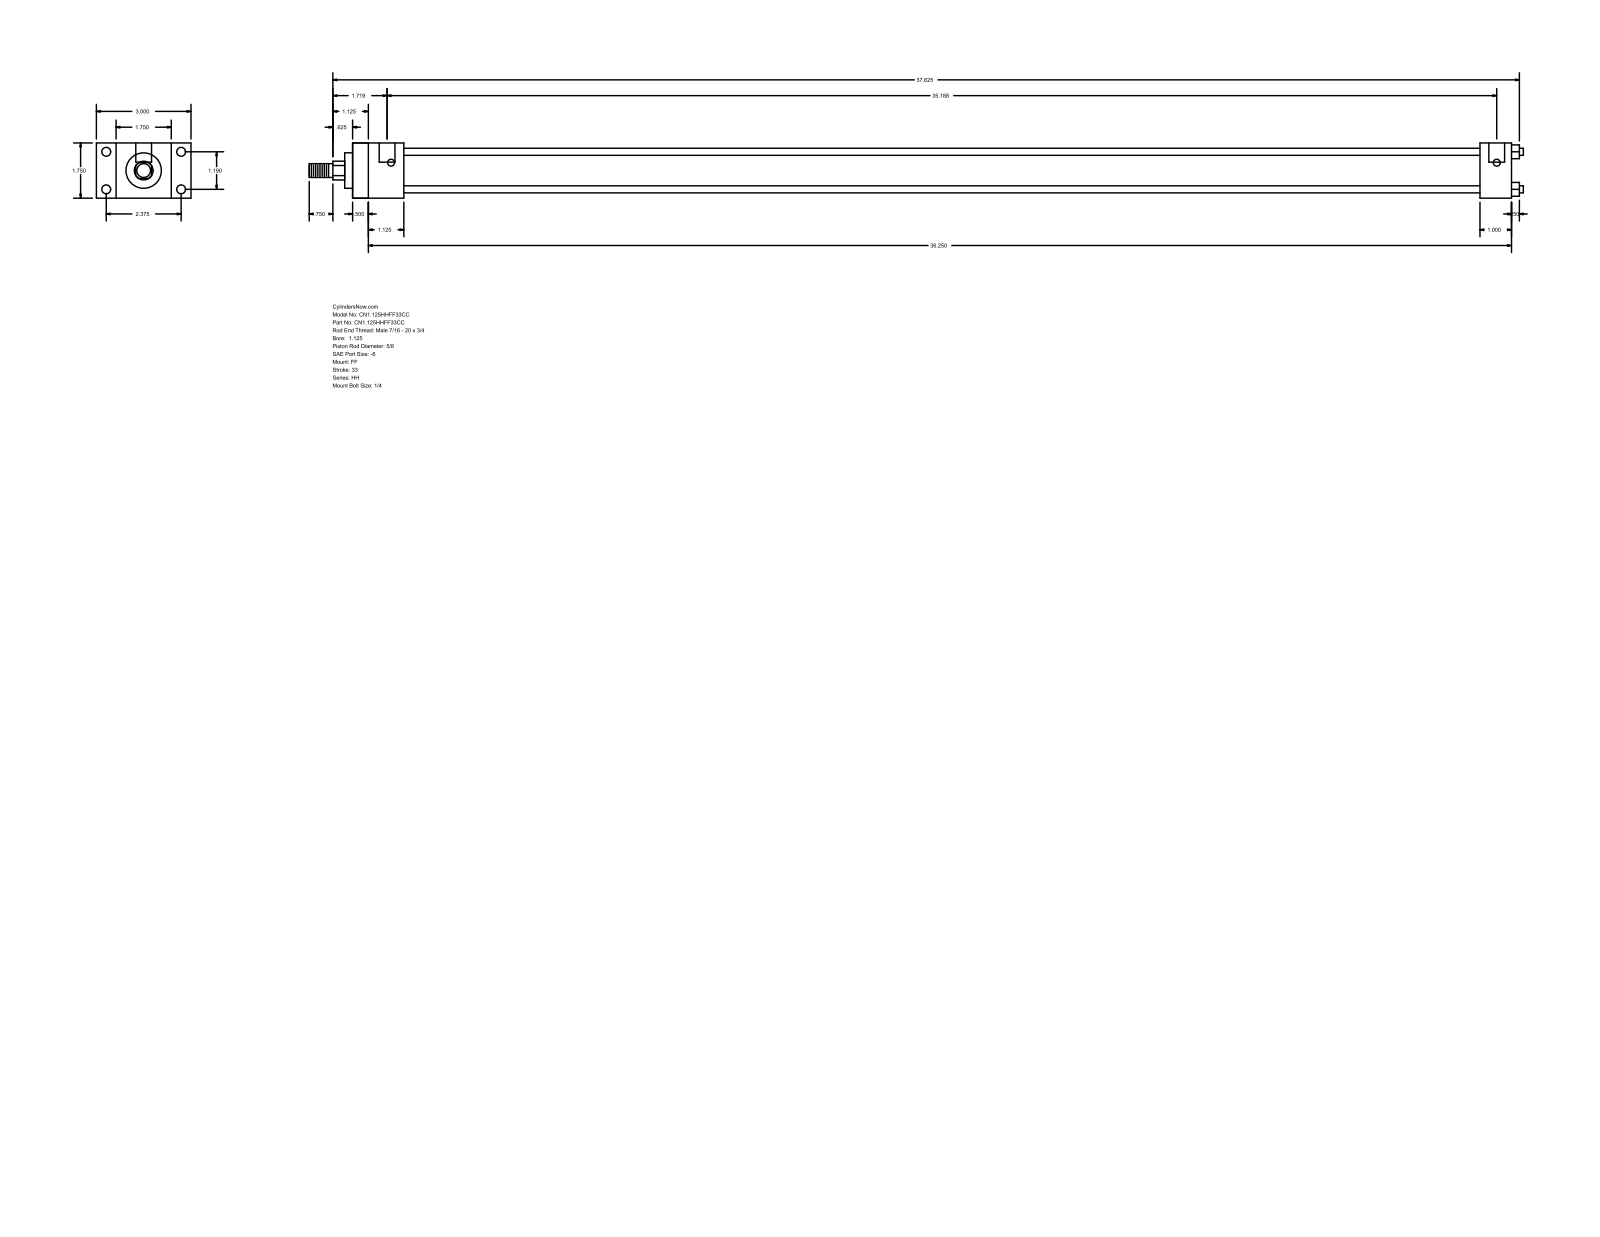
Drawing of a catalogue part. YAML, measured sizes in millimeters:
part_name: "HH_FF__0112_0.625"
step_written_by: "GSSL Pune (CONFIG_CONTROL_DESIGN)"
units: millimeters
bodies: {solids: 0, faces: 92, planar: 64, cylindrical: 28, other: 0}
overall_size: [977.9, 76.2, 44.45]
round_holes:
  - {diameter: 5.56, count: 4}
  - {diameter: 7.14, count: 4}
  - {diameter: 12.7, count: 2}
round_bosses_or_shafts:
  - {diameter: 5.71, count: 4}
  - {diameter: 34.92, count: 1}
  - {diameter: 28.57, count: 1}
  - {diameter: 15.88, count: 1}
  - {diameter: 11.11, count: 1}
partial_cylinders:
  - {radius: 7.54, count: 1}
face_to_face_distances: [44.46, 933.45, 12.69, 920.76, 15.87, 28.58, 60.33, 41.27, 908.04, 895.35]
hole_center_spacings: [30.22, 60.32, 67.47, 890.59, 3.17, 893.76]
